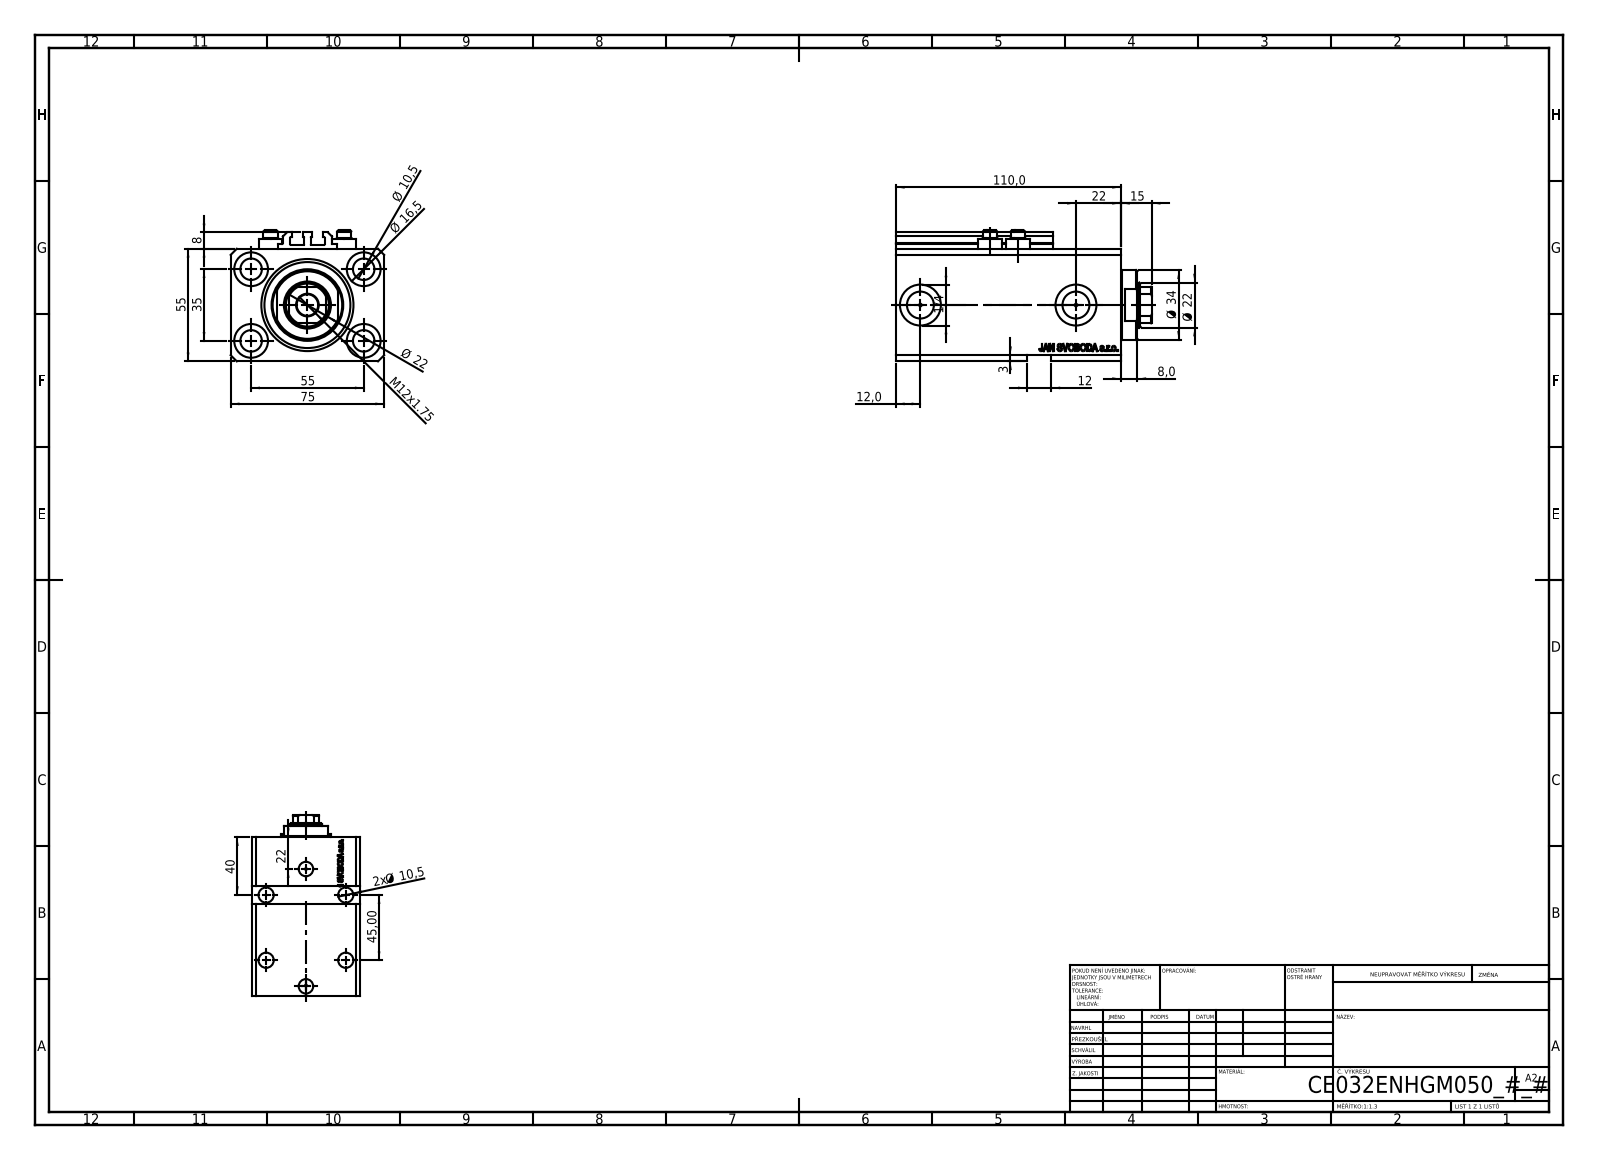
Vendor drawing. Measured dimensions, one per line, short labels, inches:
name: V250CE_VC_E; ALLEN BOLT V250CE; V250CE_E_Body; V250CE_C_VCP
written by: SolidWorks 2019 (CONFIG_CONTROL_DESIGN)
unit: in
bodies: 8 solids, 1084 faces (514 planar, 146 cylindrical, 424 other)
size: 4.921 × 2.953 × 2.52
volume: 23.27 in³; area: 148.2 in²
holes: 9× ⌀0.413, 4× ⌀0.049, 4× ⌀0.157, 4× ⌀0.65, 2× ⌀0.394, 2× ⌀0.518, 2× ⌀0.787, 1× ⌀0.866, 1× ⌀1.26, 1× ⌀1.772
bosses: 4× ⌀0.457, 4× ⌀0.276, 1× ⌀1.339
rounds: 10× R0.008, 1× R0.413
face distances: 2.165, 2.953, 0.591, 4.331, 3.74, 0.118, 0.39, 3.35, 3.941, 2.244
hole spacings: 1.283, 1.294, 2.165, 2.706, 0.535, 0.555, 0.907, 1.016
